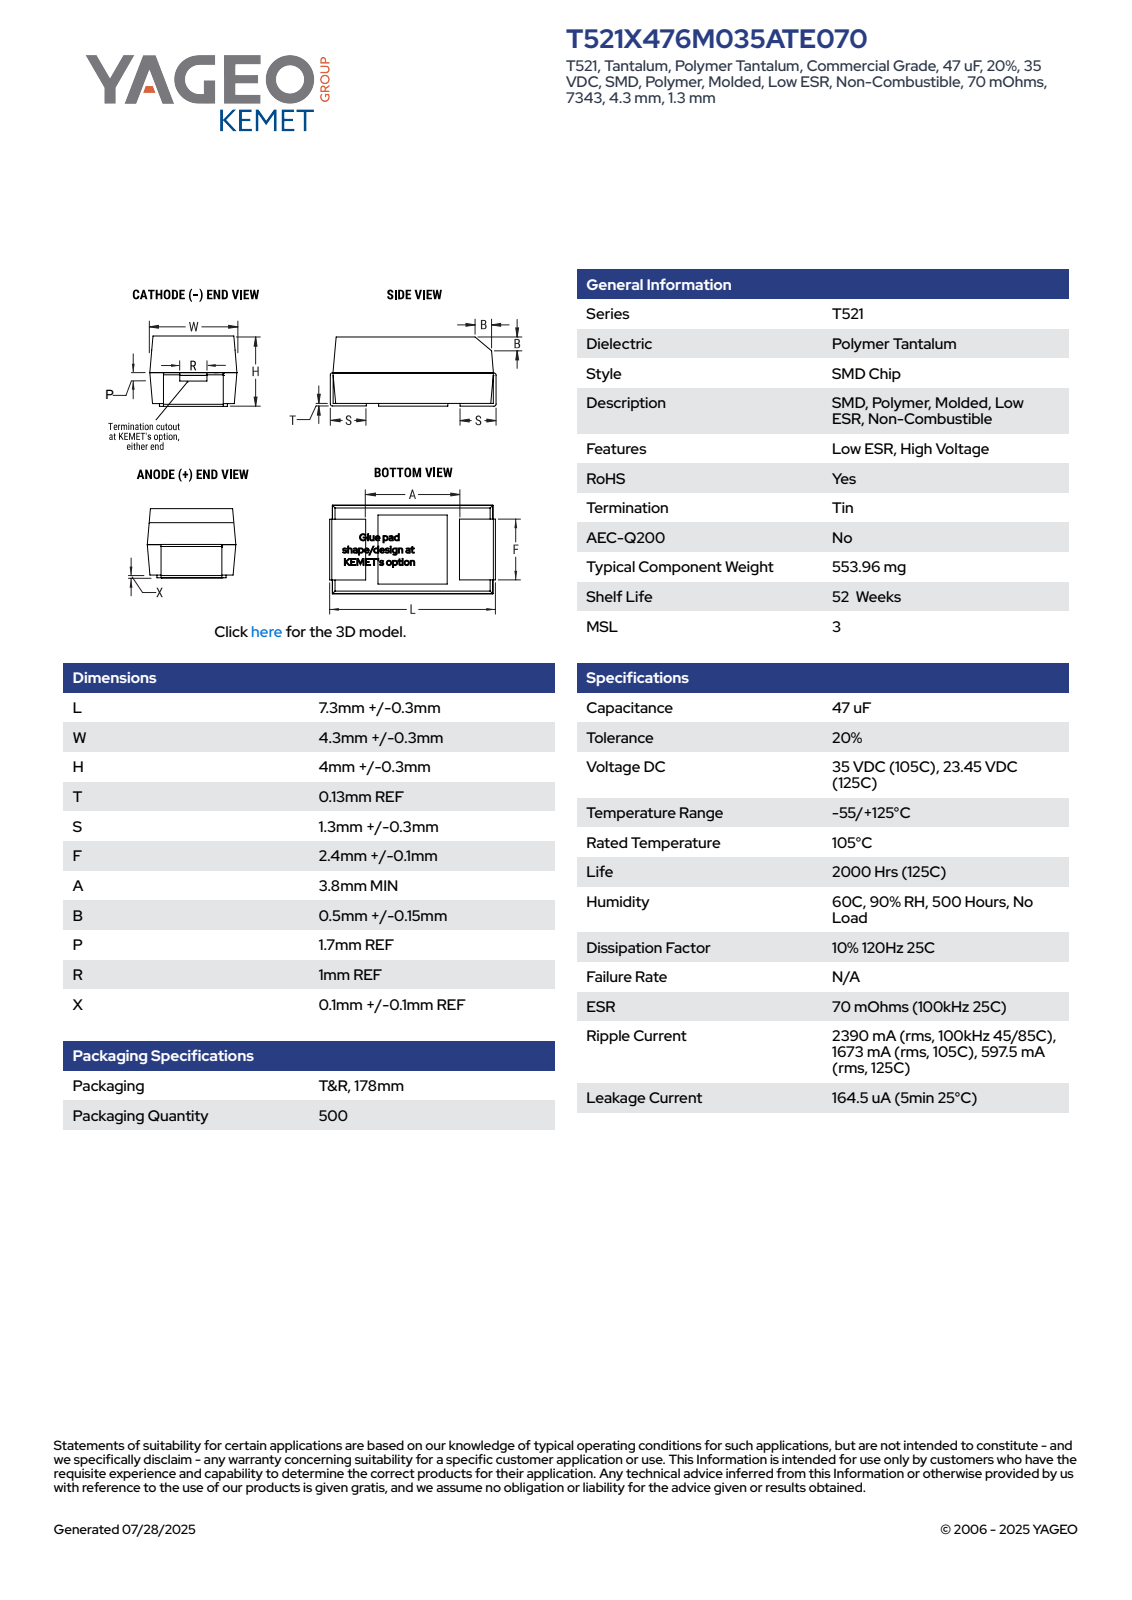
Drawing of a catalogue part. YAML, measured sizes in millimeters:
part_name: "CTSM_TCM2NKKO_7343_L7.6W4.6H4.3T0.13S1.3F2.5A3.6B0.65P1.7R1X0.1"
step_written_by: "SolidWorks 2021 (AUTOMOTIVE_DESIGN)"
units: millimeters
bodies: {solids: 4, faces: 100, planar: 95, cylindrical: 5, other: 0}
overall_size: [7.6, 4.6, 4.33]
volume: 131
surface_area: 177
partial_cylinders:
  - {radius: 0.1, count: 4}
face_to_face_distances: [4.57, 4.2, 4.3, 7.47, 4.33, 7.6, 7.34, 2.5, 2.4, 5.2]
